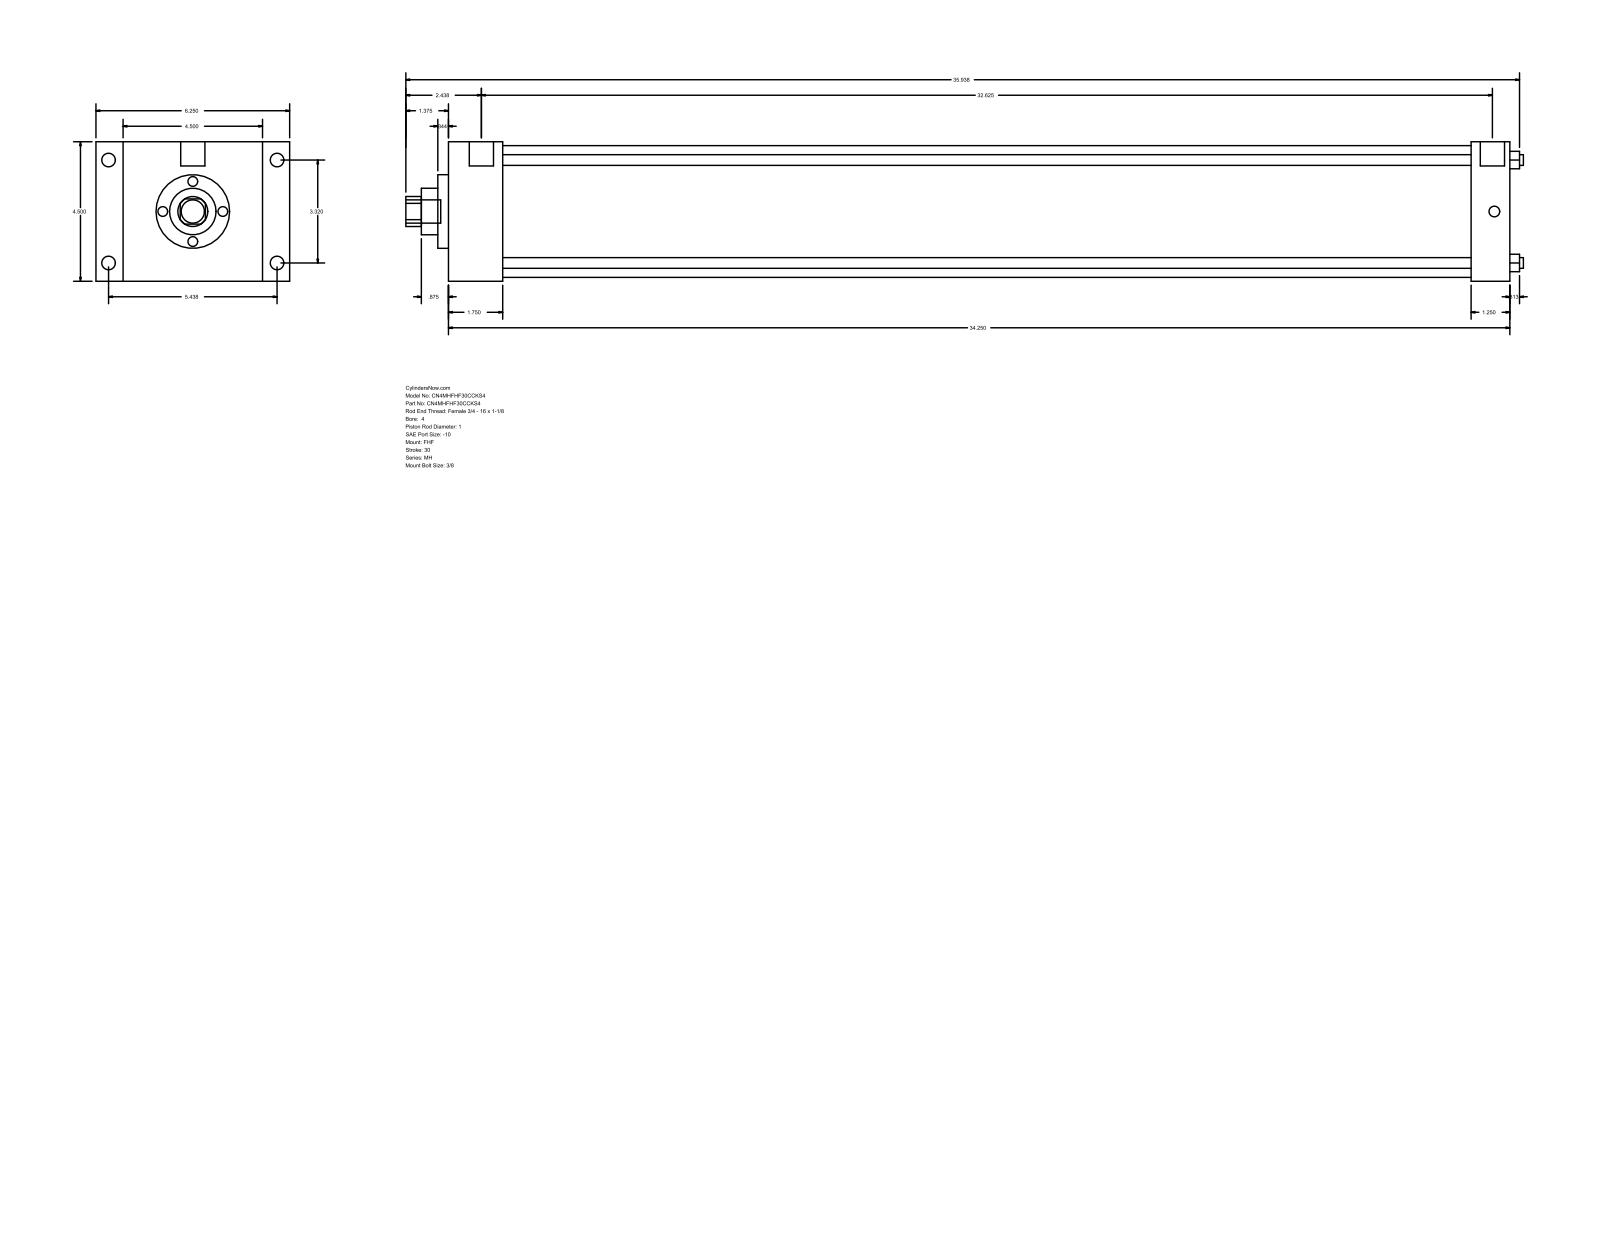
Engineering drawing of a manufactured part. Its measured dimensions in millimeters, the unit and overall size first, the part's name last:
Units: millimetres
Overall size (bounding box): 915.99 × 158.75 × 114.3
Round holes (diameter × count): ⌀8.76 ×4, ⌀25.4 ×1, ⌀38.1 ×1, ⌀60.33 ×1, ⌀107.95 ×1
Round bosses / shafts (diameter × count): ⌀11.13 ×4, ⌀8.73 ×4, ⌀19.84 ×2, ⌀19.05 ×1
Partial cylindrical surfaces — rounded edges, fillets, slot ends (radius × count): R12.29 ×1
Main face-to-face distances: 114.3, 869.96, 44.46, 825.5, 22.23, 136.53, 158.76, 838.2, 793.74, 31.76
Hole centre spacings: 59.62, 84.32, 119.25
Bodies: 0 solids, 90 faces (61 planar, 29 cylindrical, 0 other)
Part name (STEP PRODUCT): MH_FHF__0400_1
STEP written by: GSSL Pune (CONFIG_CONTROL_DESIGN)
